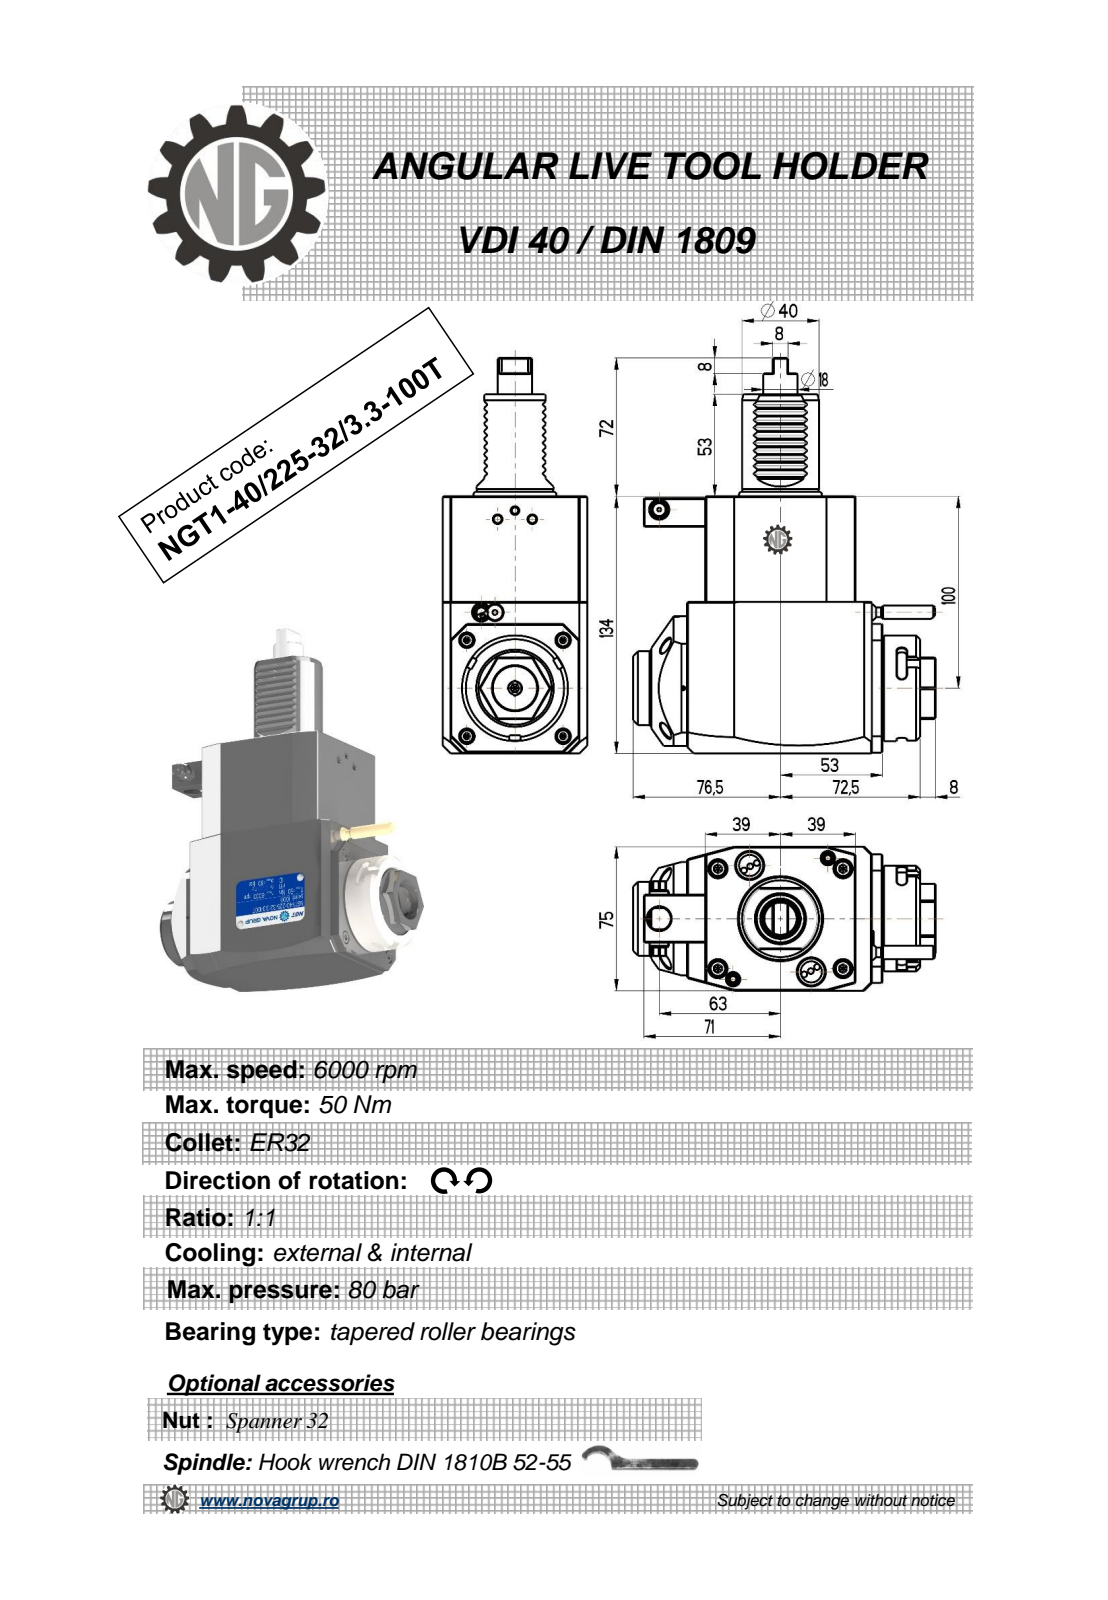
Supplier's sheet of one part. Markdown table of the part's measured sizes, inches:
| quantity | value |
| --- | --- |
| part name | NGT1_40_225_32_3_3_100T |
| STEP written by | PRO/ENGINEER BY PARAMETRIC TECHNOLOGY CORPORATION, 2010280 (CONFIG_CONTROL_DESIGN) |
| units | inches |
| bodies | 1 solid, 392 faces (223 planar, 91 cylindrical, 78 other) |
| overall size | 8.11 × 6.181 × 2.953 |
| volume | 65.72 in³ |
| surface area | 121.4 in² |
| round holes (diameter × count) | 0.079 × 1, 0.098 × 1, 0.118 × 1, 0.374 × 1, 0.472 × 1, 0.906 × 1 |
| round bosses / shafts (diameter × count) | 0.315 × 2, 2.165 × 1, 1.89 × 1, 1.575 × 1, 1.516 × 1, 0.701 × 1, 0.394 × 1, 0.276 × 1 |
| partial cylindrical surfaces (radius × count) | 0.012 × 20, 0.098 × 6, 0.031 × 2, 7.087 × 2, 0.152 × 1, 0.167 × 1, 0.965 × 1, 1.476 × 1 |
| main face-to-face distances | 2.953, 5.276, 3.071, 0.551, 3.622, 0.984, 3.342, 2.126, 4.39, 1.319 |
| hole center spacings | 1.701, 2.197, 3.642 |
